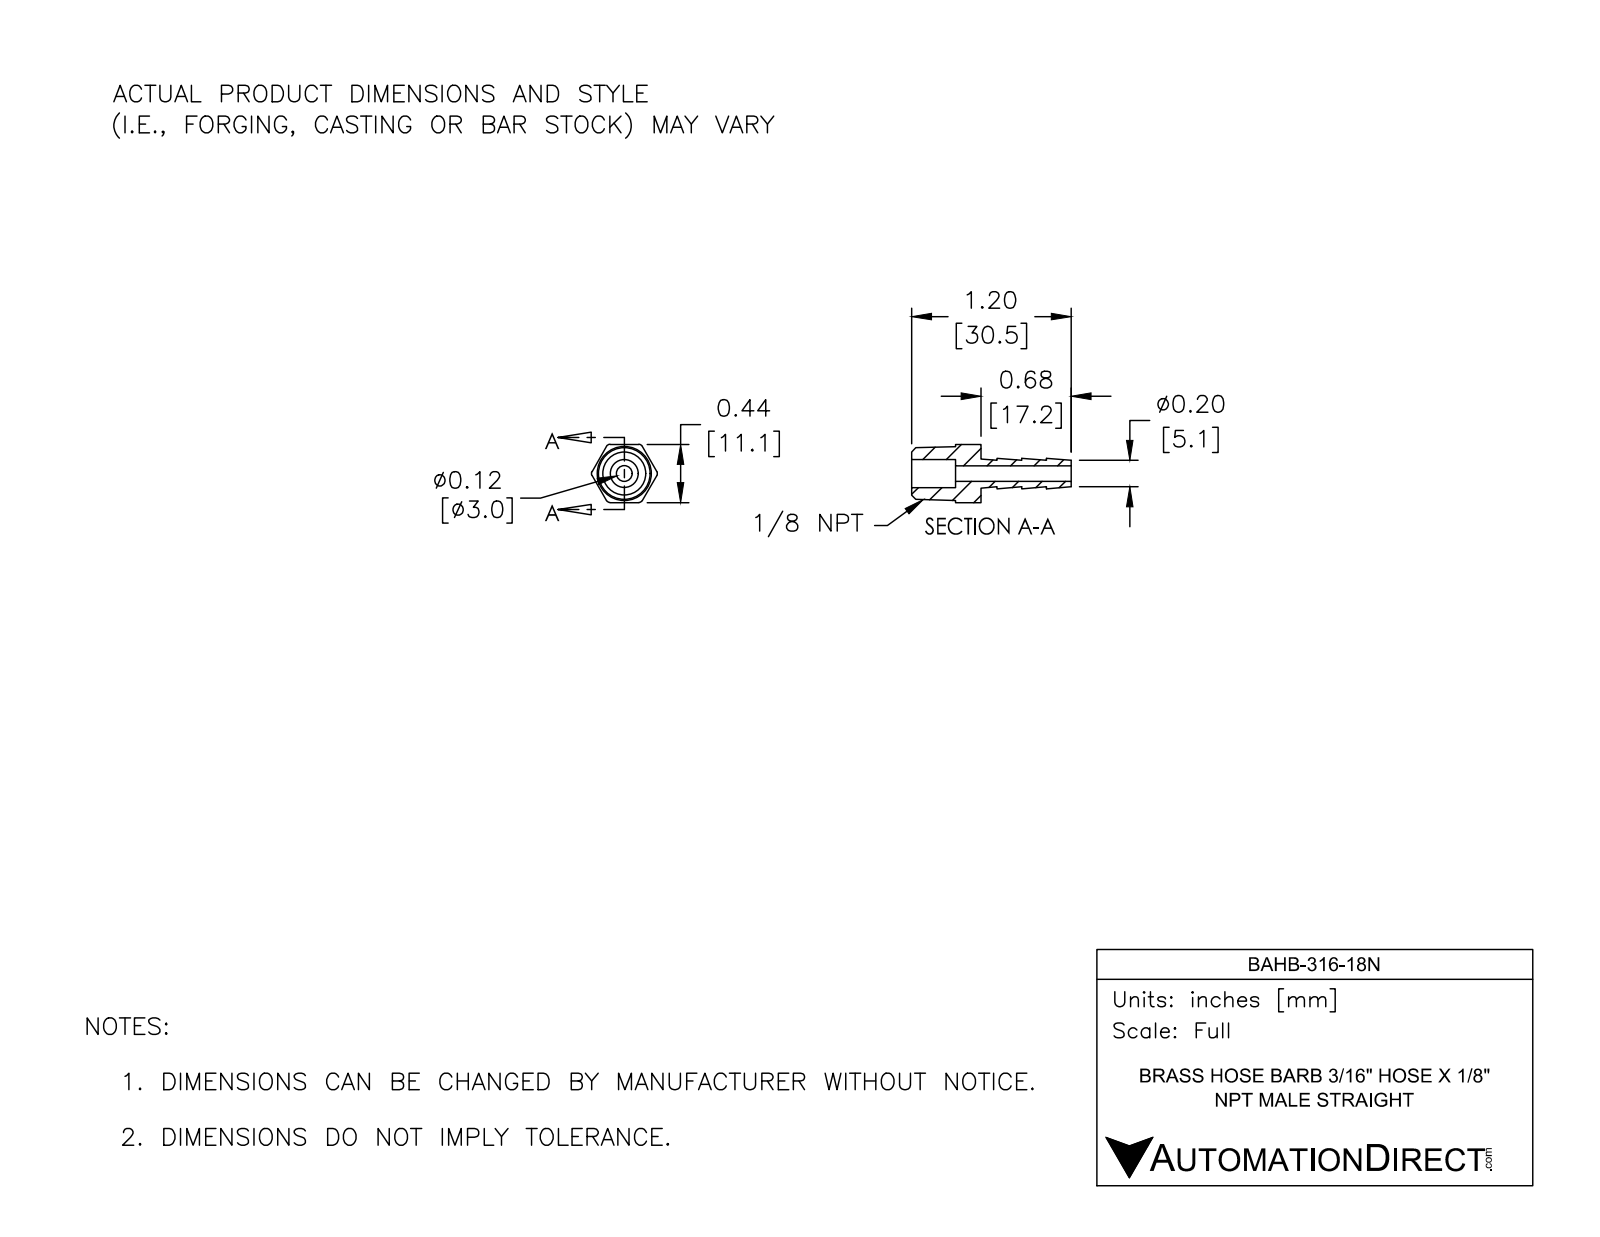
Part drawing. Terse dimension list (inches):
name: BAHB-316-18N
written by: SolidWorks 2017 (AUTOMOTIVE_DESIGN)
unit: in
bodies: 1 solid, 36 faces (14 planar, 10 cylindrical, 12 other)
size: 1.2 × 0.496 × 0.437
volume: 0.075 in³; area: 1.993 in²
holes: 1× ⌀0.117, 1× ⌀0.211
rounds: 6× R0.03
face distances: 0.438, 0.192, 0.522, 0.33, 0.186, 0.372, 0.678, 0.87, 1.2, 0.558
